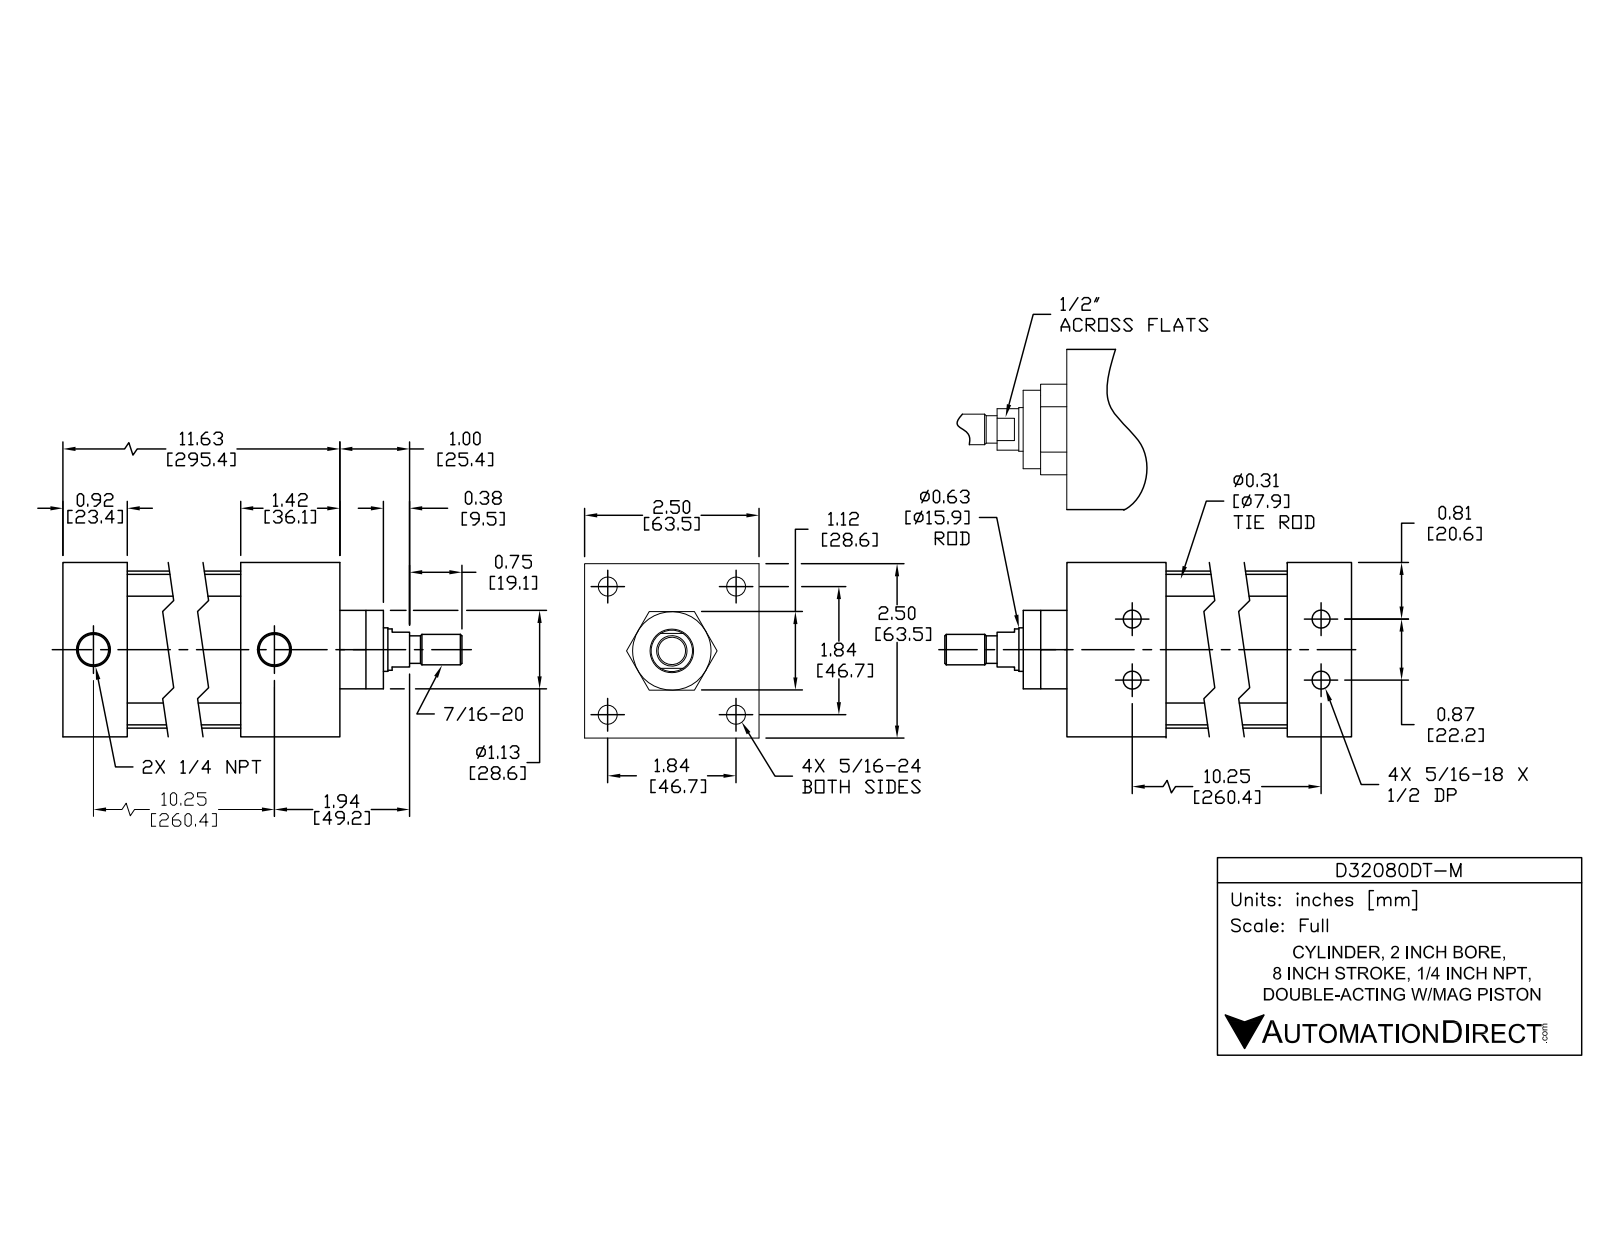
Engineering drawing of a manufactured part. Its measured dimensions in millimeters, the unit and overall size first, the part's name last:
Units: millimetres
Overall size (bounding box): 339.6 × 63.5 × 63.5
Round holes (diameter × count): ⌀6.4 ×4, ⌀6.8 ×4, ⌀9.1 ×4, ⌀12.7 ×4, ⌀7.5 ×2, ⌀12.1 ×2, ⌀15.9 ×1, ⌀16 ×1, ⌀50.8 ×1
Round bosses / shafts (diameter × count): ⌀12.3 ×4, ⌀8 ×4, ⌀7.2 ×4, ⌀57.2 ×1, ⌀50.7 ×1, ⌀28.4 ×1, ⌀15.8 ×1, ⌀15 ×1
Partial cylindrical surfaces — rounded edges, fillets, slot ends (radius × count): R6.4 ×4
Main face-to-face distances: 63.5, 295.2, 36.1, 259.1, 235.7, 271.8, 23.4, 25.4, 269.3, 233.2
Hole centre spacings: 11.1, 33.2, 46.9, 260.5, 260.2, 22.2, 66.4, 261.2
Volume: 507 000 mm³ · Surface area: 177 000 mm²
Bodies: 12 solids, 298 faces (94 planar, 114 cylindrical, 90 other)
Part name (STEP PRODUCT): D32080DT-M PISTON; D32080DT-M; D32080DT-M BODY
STEP written by: SolidWorks 2015 (AUTOMOTIVE_DESIGN)
